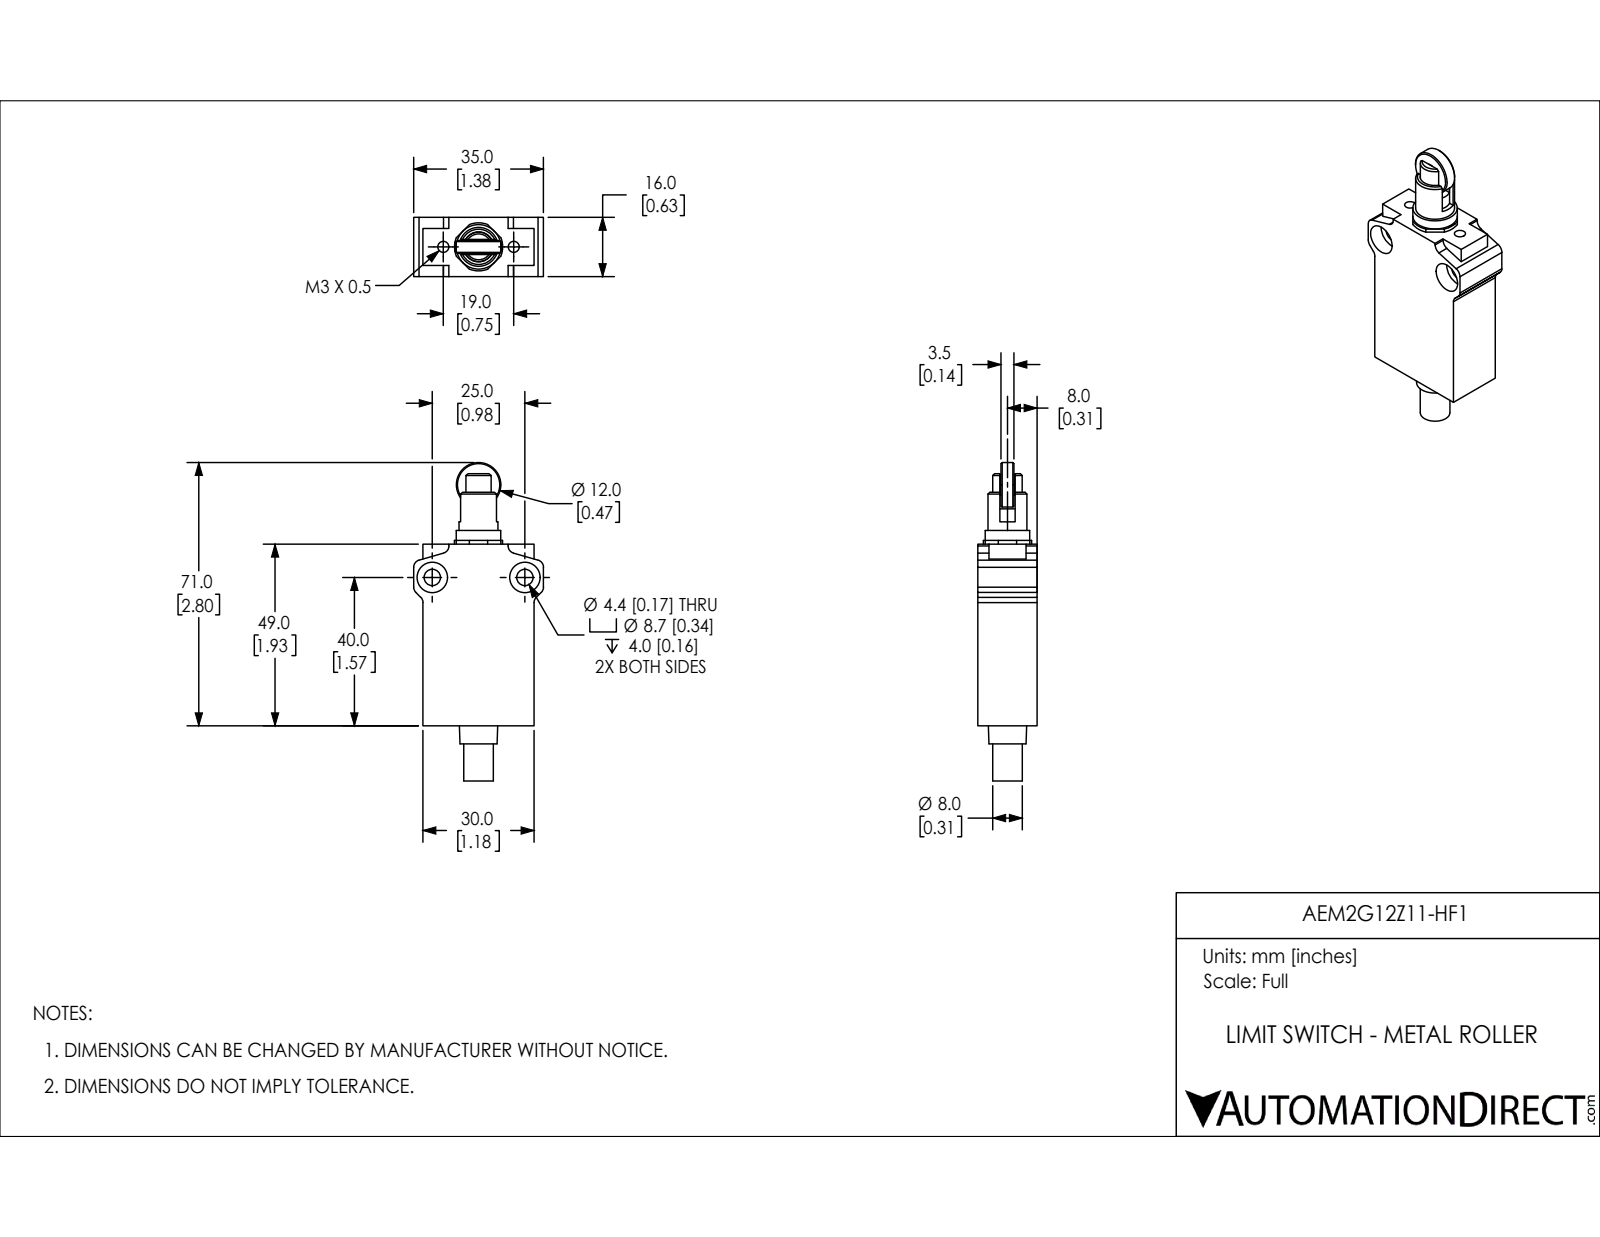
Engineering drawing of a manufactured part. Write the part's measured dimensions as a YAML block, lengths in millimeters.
part_name: "AEM2G12Z11-HF1"
step_written_by: "SolidWorks 2018 (AUTOMOTIVE_DESIGN)"
units: millimeters
bodies: {solids: 0, faces: 144, planar: 64, cylindrical: 65, other: 15}
overall_size: [85.9, 35, 16]
round_holes:
  - {diameter: 3, count: 2}
  - {diameter: 4.4, count: 2}
  - {diameter: 8.2, count: 2}
  - {diameter: 8.1, count: 1}
round_bosses_or_shafts:
  - {diameter: 12, count: 2}
  - {diameter: 10.5, count: 1}
  - {diameter: 8, count: 1}
  - {diameter: 8, count: 1}
  - {diameter: 5.6, count: 1}
partial_cylinders:
  - {radius: 2, count: 8}
  - {radius: 6.5, count: 1}
face_to_face_distances: [16, 30, 3.8, 1, 49, 12, 5.9, 4, 6, 10.1]
hole_center_spacings: [9.5, 19, 25]
